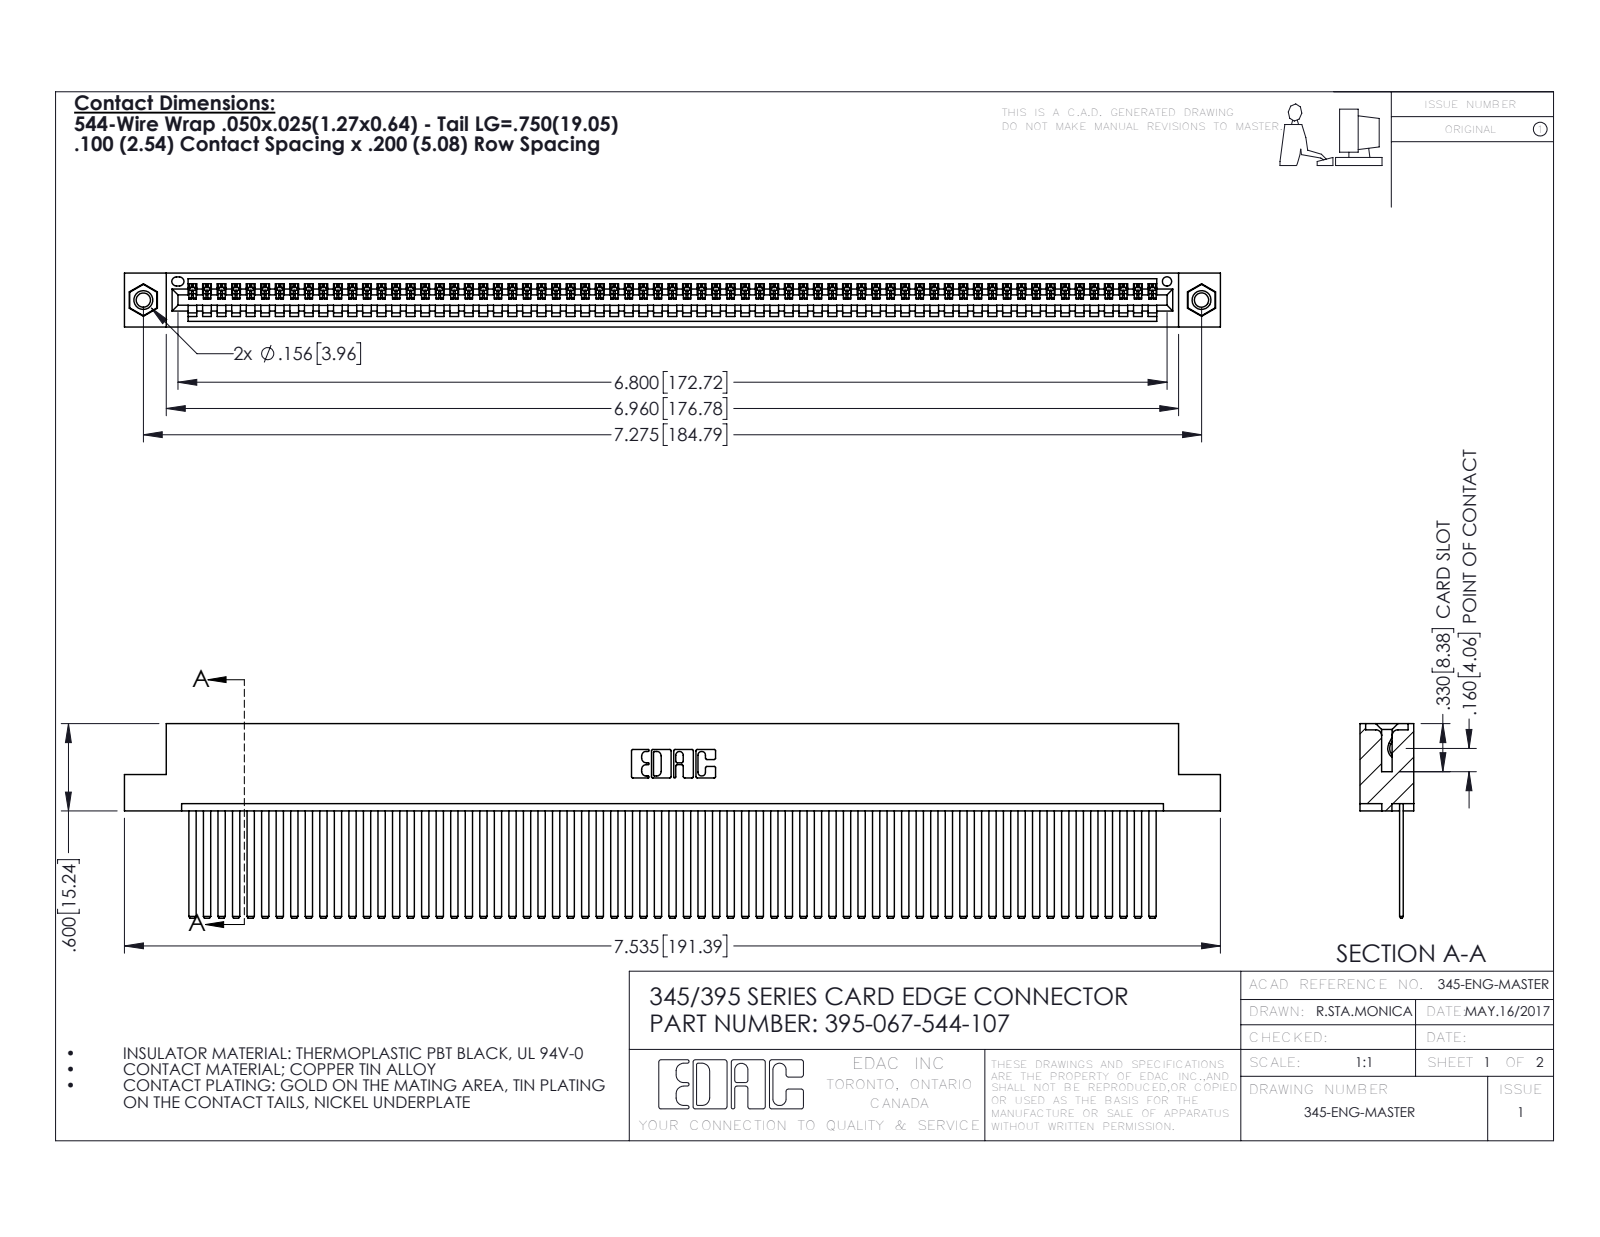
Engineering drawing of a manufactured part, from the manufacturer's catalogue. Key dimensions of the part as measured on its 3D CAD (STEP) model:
Part name (STEP PRODUCT): 345-250-001_345-250-005-103; 345 Part_Flush Mounting Lugs - 0.156 Dia-TI; 345-292-001_345-293-144; 395-067-544-107
STEP written by: SolidWorks 2016 (CONFIG_CONTROL_DESIGN)
Units: inches
Bodies: 70 solids, 3670 faces (2524 planar, 1130 cylindrical, 16 other)
Overall size (bounding box): 7.535 × 1.337 × 0.37
Volume: 1.168 in³ · Surface area: 43.62 in²
Round holes (diameter × count): ⌀0.098 ×2, ⌀0.125 ×2, ⌀0.156 ×2, ⌀0.064 ×1
Round bosses / shafts (diameter × count): ⌀0.155 ×2
Partial cylindrical surfaces — rounded edges, fillets, slot ends (radius × count): R0.006 ×134, R0.01 ×22, R0.007 ×6, R0.031 ×6, R0.026 ×3, R0.031 ×2, R0.04 ×2, R0.014 ×1
Main face-to-face distances: 0.072, 0.298, 0.025, 0.098, 0.272, 0.37, 0.2, 0.225, 0.149, 0.072
Hole centre spacings: 0.27, 7.039, 7.275
